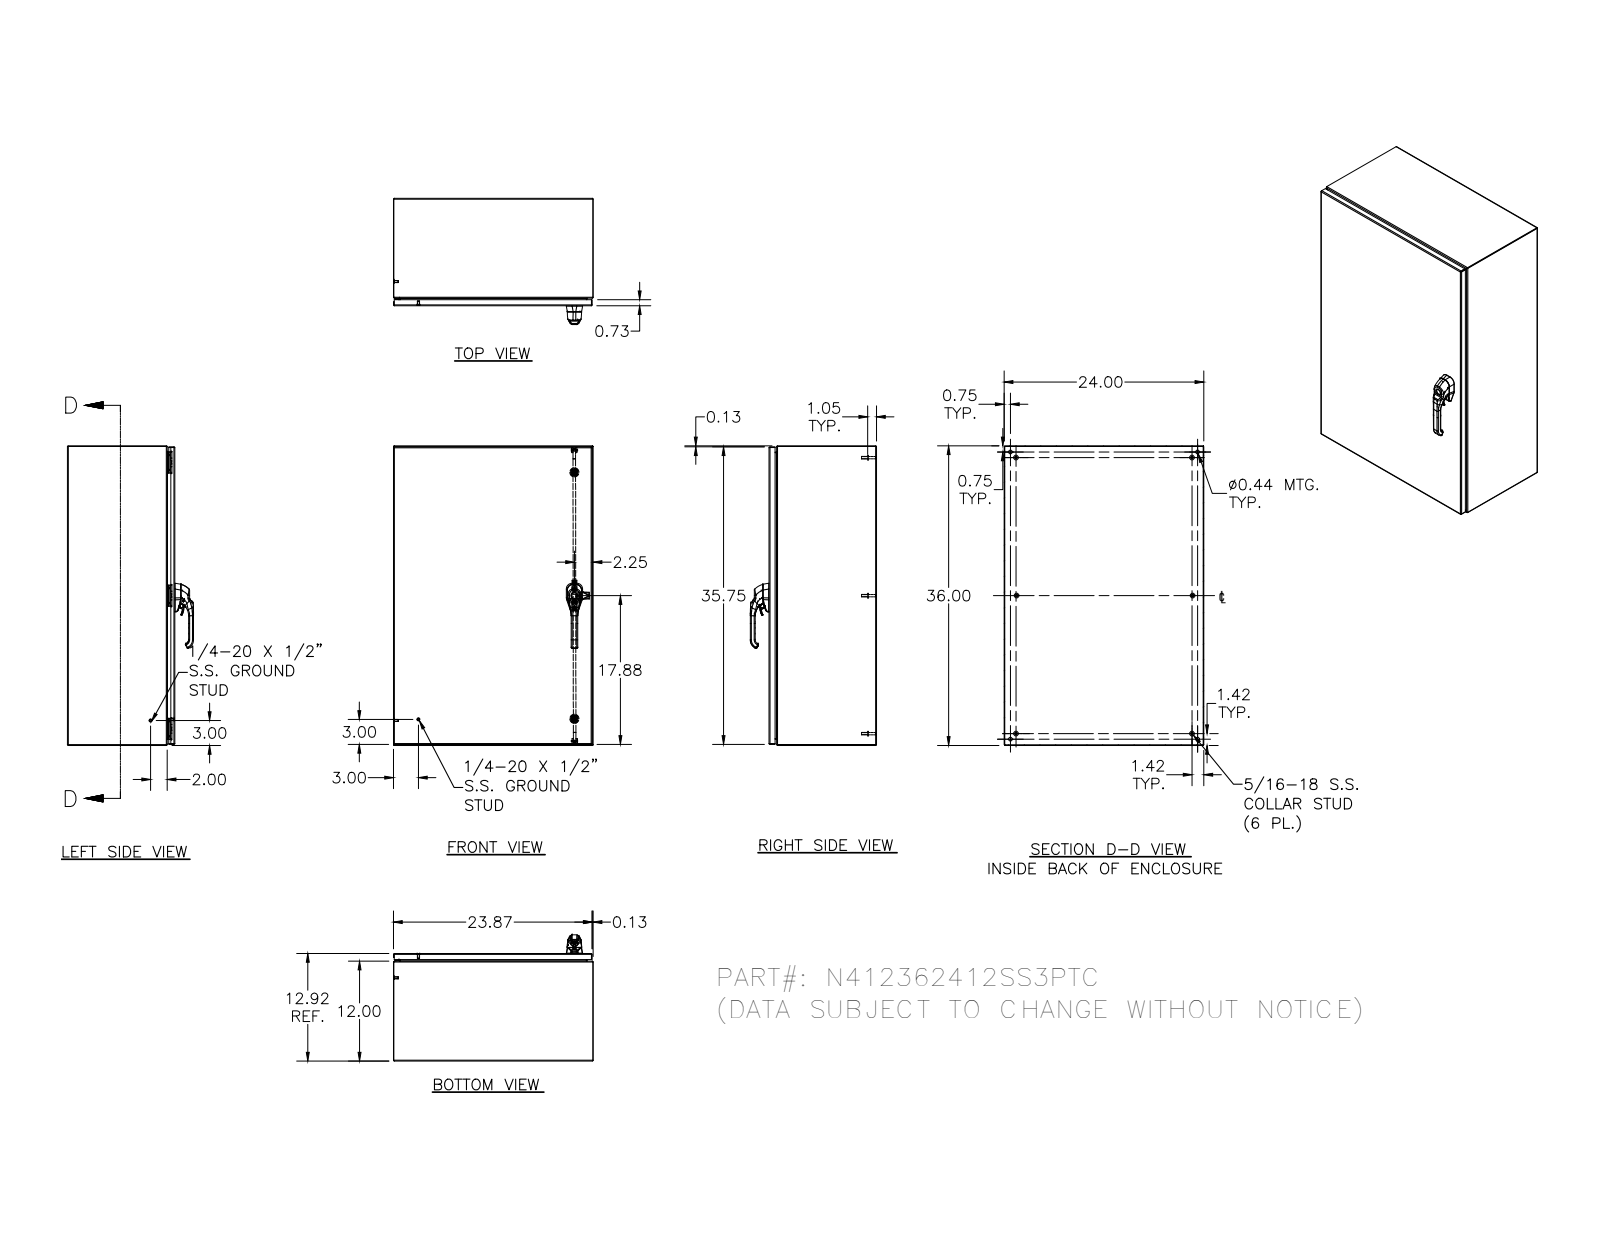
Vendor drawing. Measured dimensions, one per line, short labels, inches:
name: N412362412SS3PTC; N412362412SS3PTCBKP; N4123624SS3PTCLID; HFW328176 (+8 more)
written by: Autodesk Inventor 2011 (AUTOMOTIVE_DESIGN)
unit: in
bodies: 74 solids, 3522 faces (1171 planar, 1295 cylindrical, 1056 other)
size: 36 × 24 × 15.166
volume: 263.9 in³; area: 7 007 in²
holes: 6× ⌀0.093, 6× ⌀0.152, 6× ⌀0.167, 6× ⌀0.172, 6× ⌀0.188, 5× ⌀0.165, 4× ⌀0.197, 4× ⌀0.437, 3× ⌀0.156, 3× ⌀0.213, 2× ⌀0.106, 2× ⌀0.16
bosses: 14× ⌀0.25, 6× ⌀0.563, 6× ⌀0.36, 6× ⌀0.32, 6× ⌀0.3, 6× ⌀0.275, 6× ⌀0.256, 6× ⌀0.236
rounds: 178× R0.02, 101× R0.012, 38× R0.05, 34× R0.031, 26× R0.016, 23× R0.118, 21× R0.019, 21× R0.125
face distances: 0.074, 12.843, 23.926, 12.769, 12.917, 35.926, 23.852, 24, 36, 35.852
hole spacings: 16, 15.996, 31.996, 16.008, 0.017, 0.66, 16.656, 22.869
